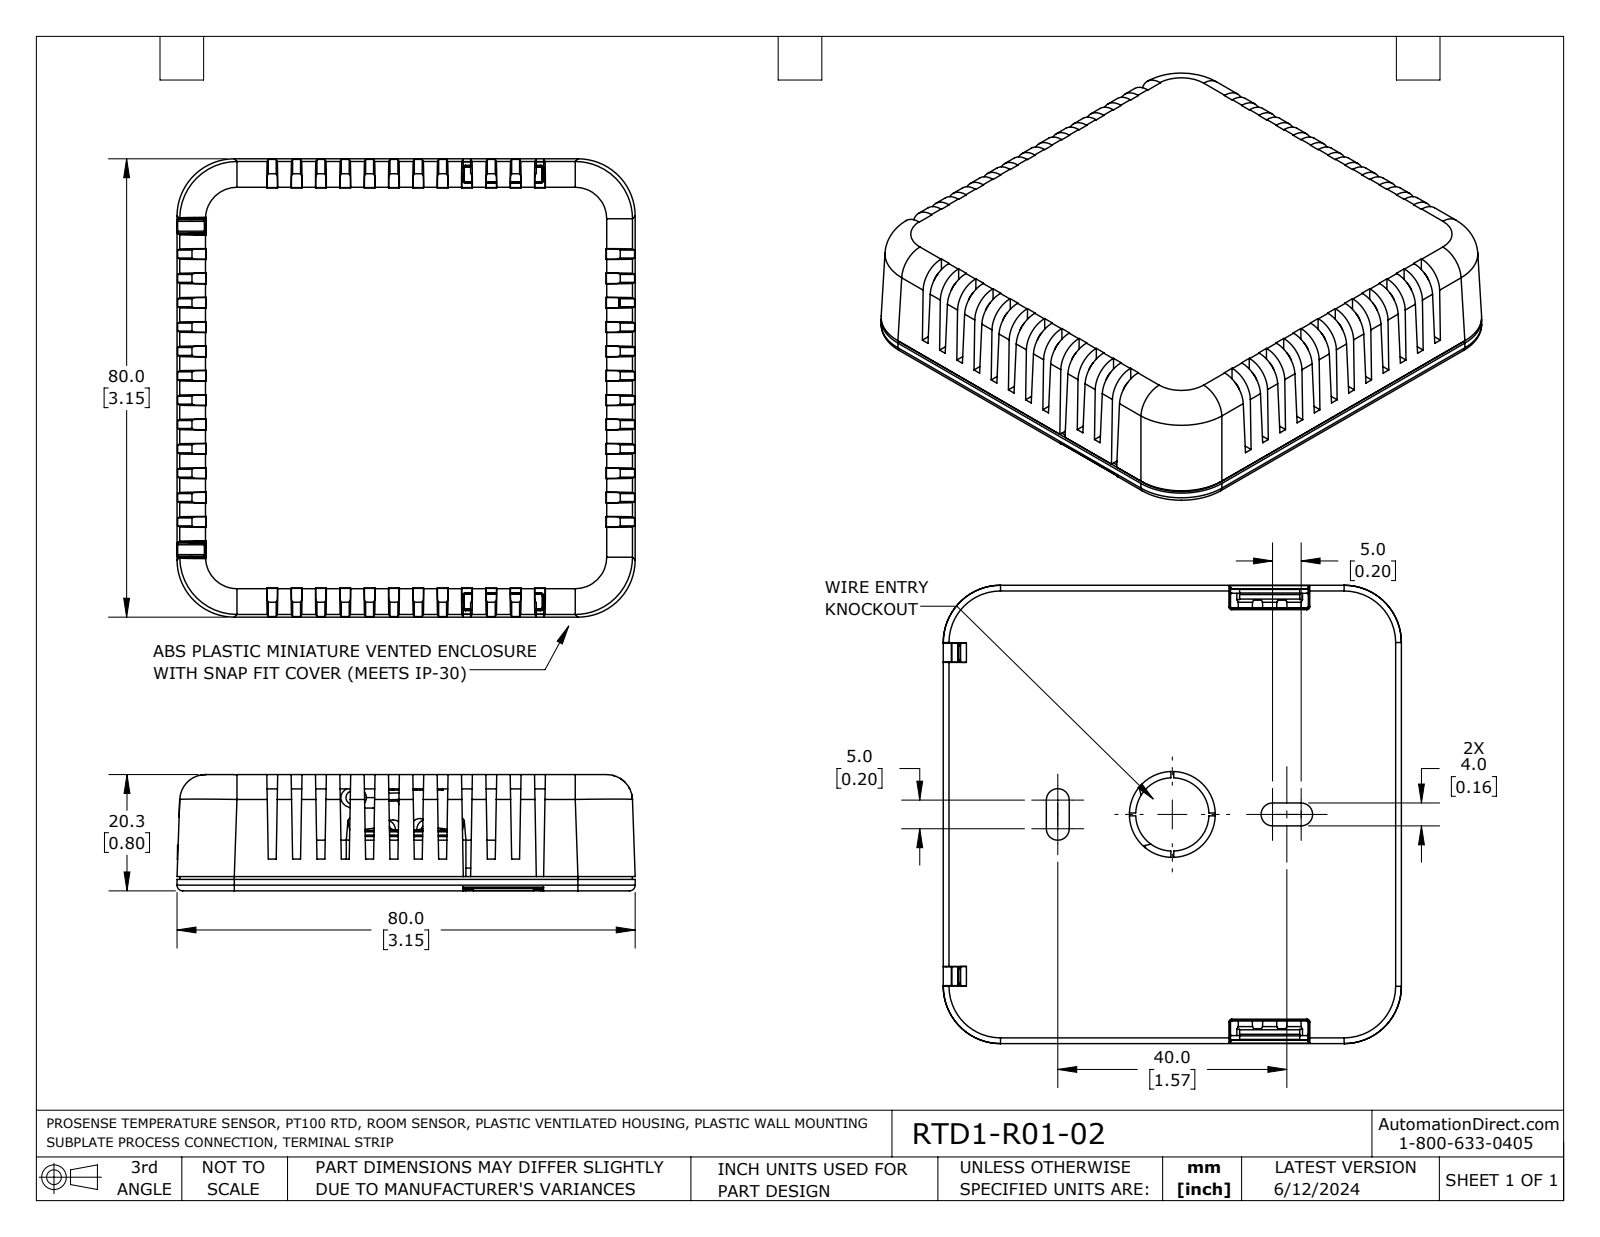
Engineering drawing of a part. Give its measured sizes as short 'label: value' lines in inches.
name: RTD1-R01-02
written by: SolidWorks 2021 (AUTOMOTIVE_DESIGN)
unit: in
bodies: 15 solids, 1372 faces (792 planar, 313 cylindrical, 267 other)
size: 3.15 × 3.15 × 0.799
volume: 2.542 in³; area: 66.18 in²
holes: 8× ⌀0.217, 6× ⌀0.175, 4× ⌀0.098, 2× ⌀0.07, 2× ⌀0.146, 2× ⌀0.175
bosses: 4× ⌀0.27, 4× ⌀0.17, 4× ⌀0.12, 2× ⌀0.138, 2× ⌀0.045, 2× ⌀0.045, 2× ⌀0.01
rounds: 24× R0.01, 16× R0.012, 9× R0.037, 9× R0.038, 8× R0.145, 8× R0.394, 6× R0.03, 5× R0.039
face distances: 0.098, 0.701, 0.799, 0.602, 0.167, 0.335, 0.502, 0.669, 0.837, 1.004
hole spacings: 0.3, 0.374, 0.479, 0.748, 0.806, 0.374, 0.48, 1.121
